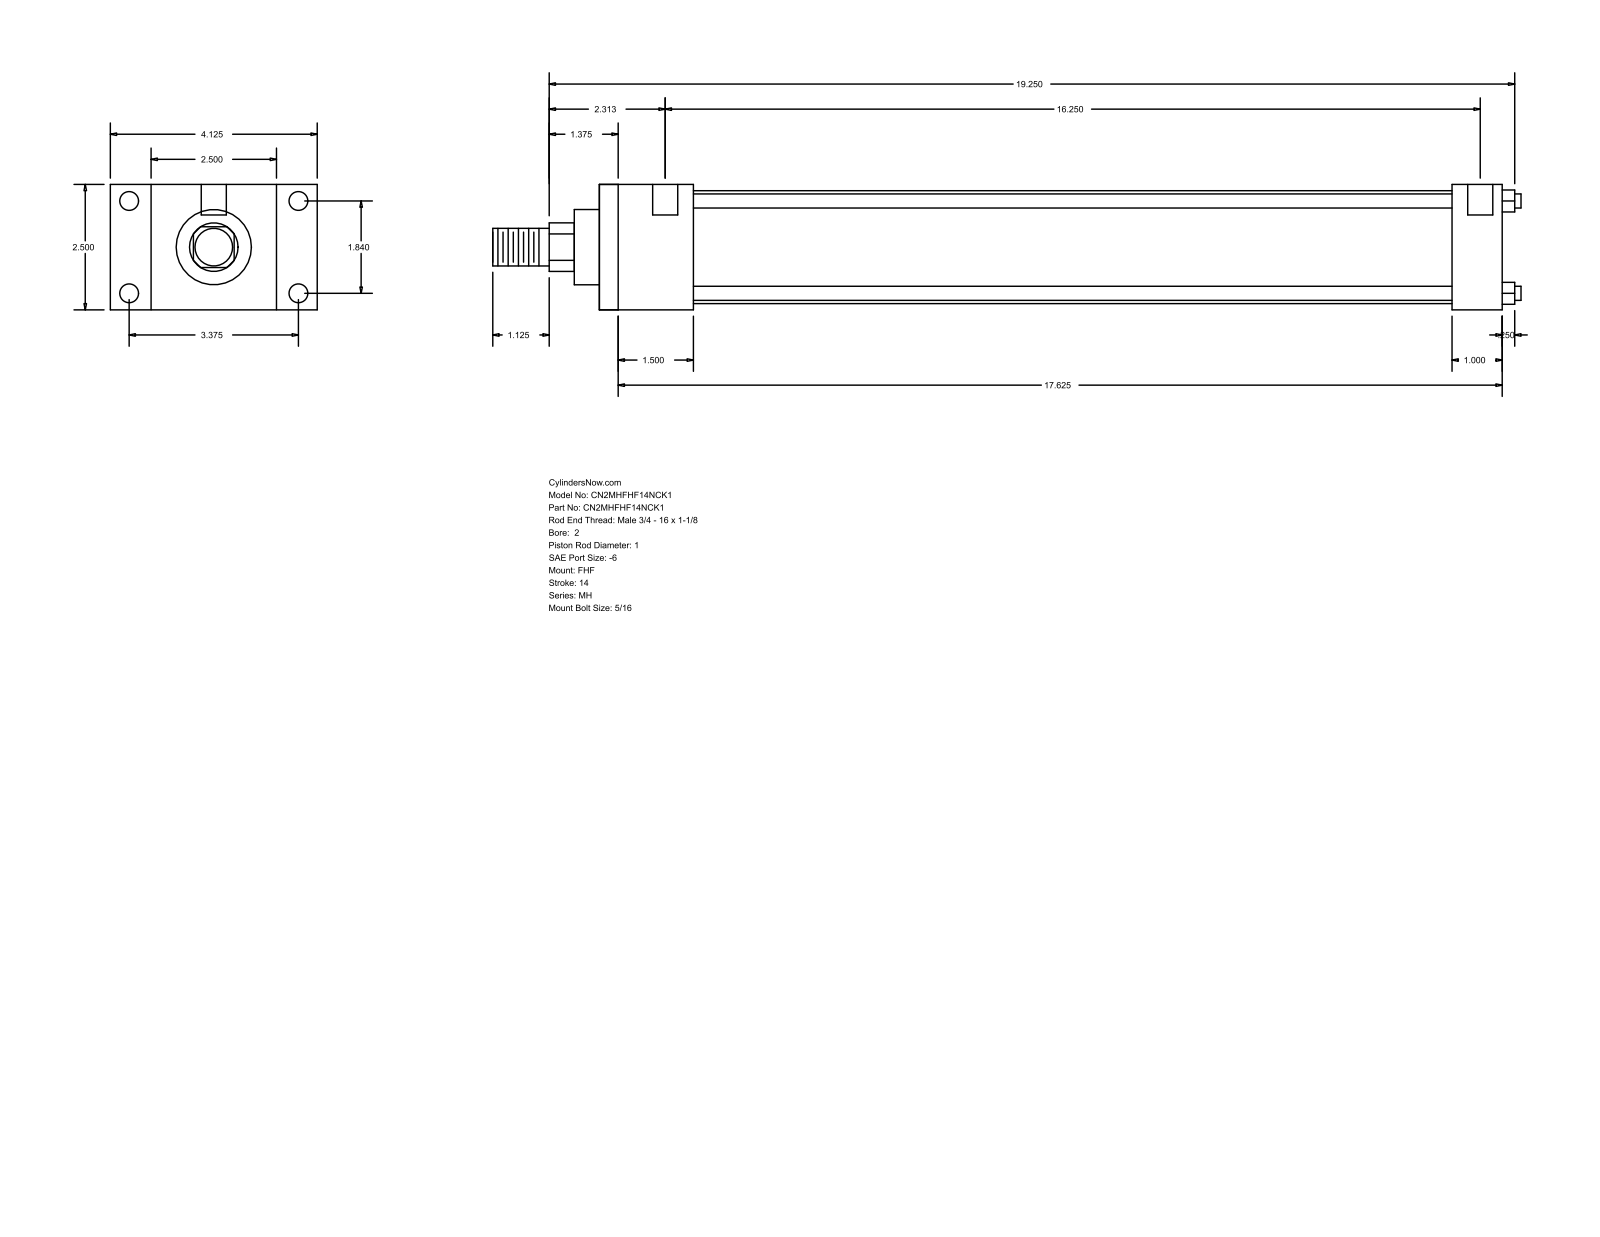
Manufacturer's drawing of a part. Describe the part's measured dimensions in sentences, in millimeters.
The part is named "MH_FHF__0200_1". Its 3-D file was written by "GSSL Pune (CONFIG_CONTROL_DESIGN)". It is 0 solids with 88 faces: 60 planar, 28 cylindrical and 0 other. Overall it measures 520.7 by 104.78 by 63.5 millimeters. Round holes: 4 of diameter 5.56, 4 of diameter 9.53, 2 of diameter 12.7. Round bosses or shafts: 4 of diameter 7.14, 1 of diameter 57.15, 1 of diameter 38.1, 1 of diameter 25.4, 1 of diameter 19.05. Partial cylindrical surfaces (rounded edges, fillets, slot ends): 1 of radius 12.29. The main face-to-face distances are 63.5, 457.2, 47.63, 409.57, 20.64, 84.14, 104.78, 25.4, 431.8, 384.17. The hole center spacings are 46.74, 85.72, 97.63, 420.68, 3.17, 4.76, 412.75, 415.92.
